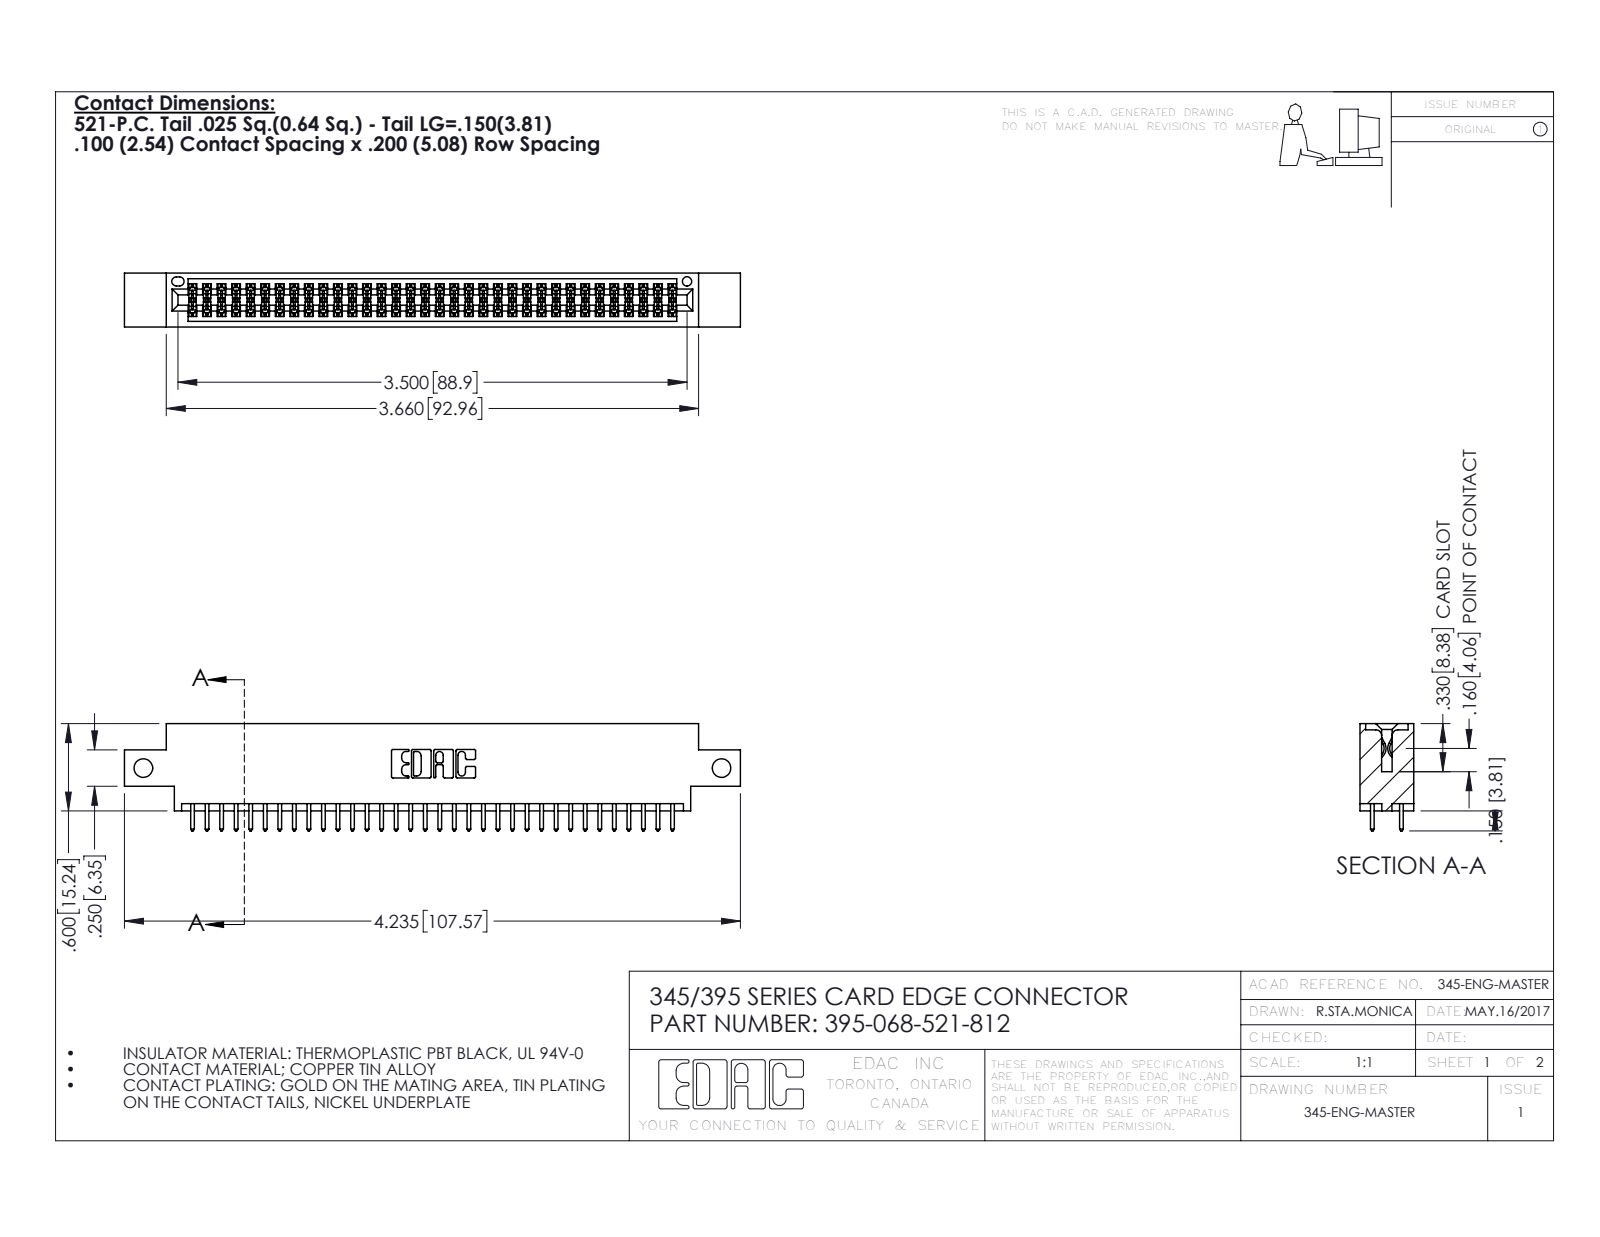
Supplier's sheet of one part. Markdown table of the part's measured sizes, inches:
| quantity | value |
| --- | --- |
| part name | 395-068-521-812; 345 Part_0.170 Offset - Side Mount; 345-292-001_345-293-121 |
| STEP written by | SolidWorks 2016 (CONFIG_CONTROL_DESIGN) |
| units | inches |
| bodies | 69 solids, 3530 faces (2328 planar, 1202 cylindrical, 0 other) |
| overall size | 4.235 × 0.737 × 0.37 |
| volume | 0.619 in³ |
| surface area | 22.74 in² |
| round holes (diameter × count) | 0.128 × 2, 0.064 × 1 |
| partial cylindrical surfaces (radius × count) | 0.006 × 102, 0.01 × 68, 0.01 × 22, 0.007 × 6, 0.031 × 6, 0.026 × 3, 0.014 × 2, 0.019 × 2 |
| main face-to-face distances | 0.298, 0.072, 0.37, 0.2, 0.098, 0.272, 0.025, 0.225, 0.175, 0.149 |
| hole center spacings | 3.975 |
